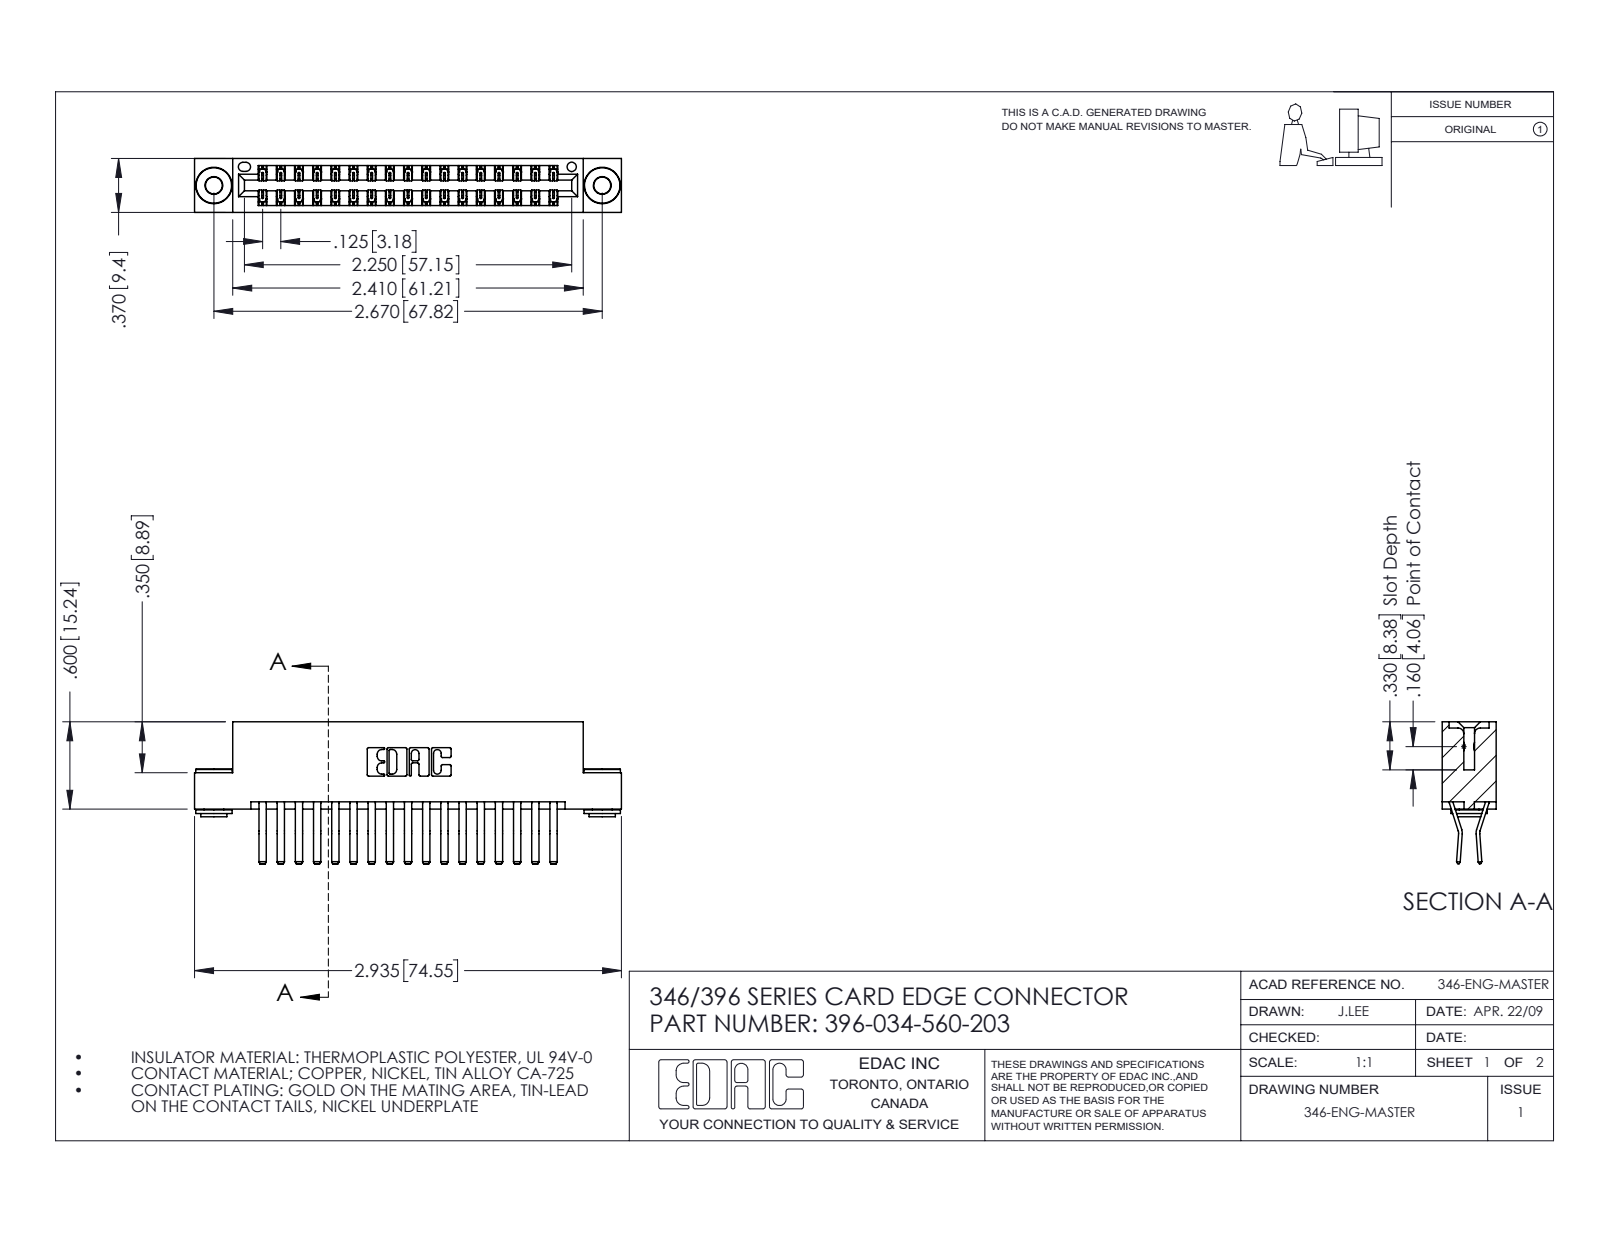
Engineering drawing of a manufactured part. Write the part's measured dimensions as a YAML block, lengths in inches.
part_name: "345-292-001_560 Tail; 346 Part_Flush Mounting Lugs - 0.156 Dia-TH; 345-250-002_345-250-002-102; 396-034-560-203"
step_written_by: "SolidWorks 2016 (CONFIG_CONTROL_DESIGN)"
units: inches
bodies: {solids: 37, faces: 1996, planar: 1276, cylindrical: 712, other: 8}
overall_size: [2.935, 0.975, 0.37]
volume: 0.447
surface_area: 16.24
round_holes:
  - {diameter: 0.116, count: 2}
  - {diameter: 0.156, count: 2}
  - {diameter: 0.064, count: 1}
round_bosses_or_shafts:
  - {diameter: 0.25, count: 2}
  - {diameter: 0.18, count: 2}
  - {diameter: 0.136, count: 2}
partial_cylinders:
  - {radius: 0.006, count: 51}
  - {radius: 0.01, count: 22}
  - {radius: 0.007, count: 6}
  - {radius: 0.031, count: 6}
  - {radius: 0.026, count: 3}
  - {radius: 0.01, count: 2}
  - {radius: 0.014, count: 2}
  - {radius: 0.022, count: 2}
face_to_face_distances: [0.048, 0.322, 0.25, 0.37, 0.025, 0.072, 0.298, 0.275, 0.148, 0.222]
hole_center_spacings: [0.246, 2.463, 2.67]
